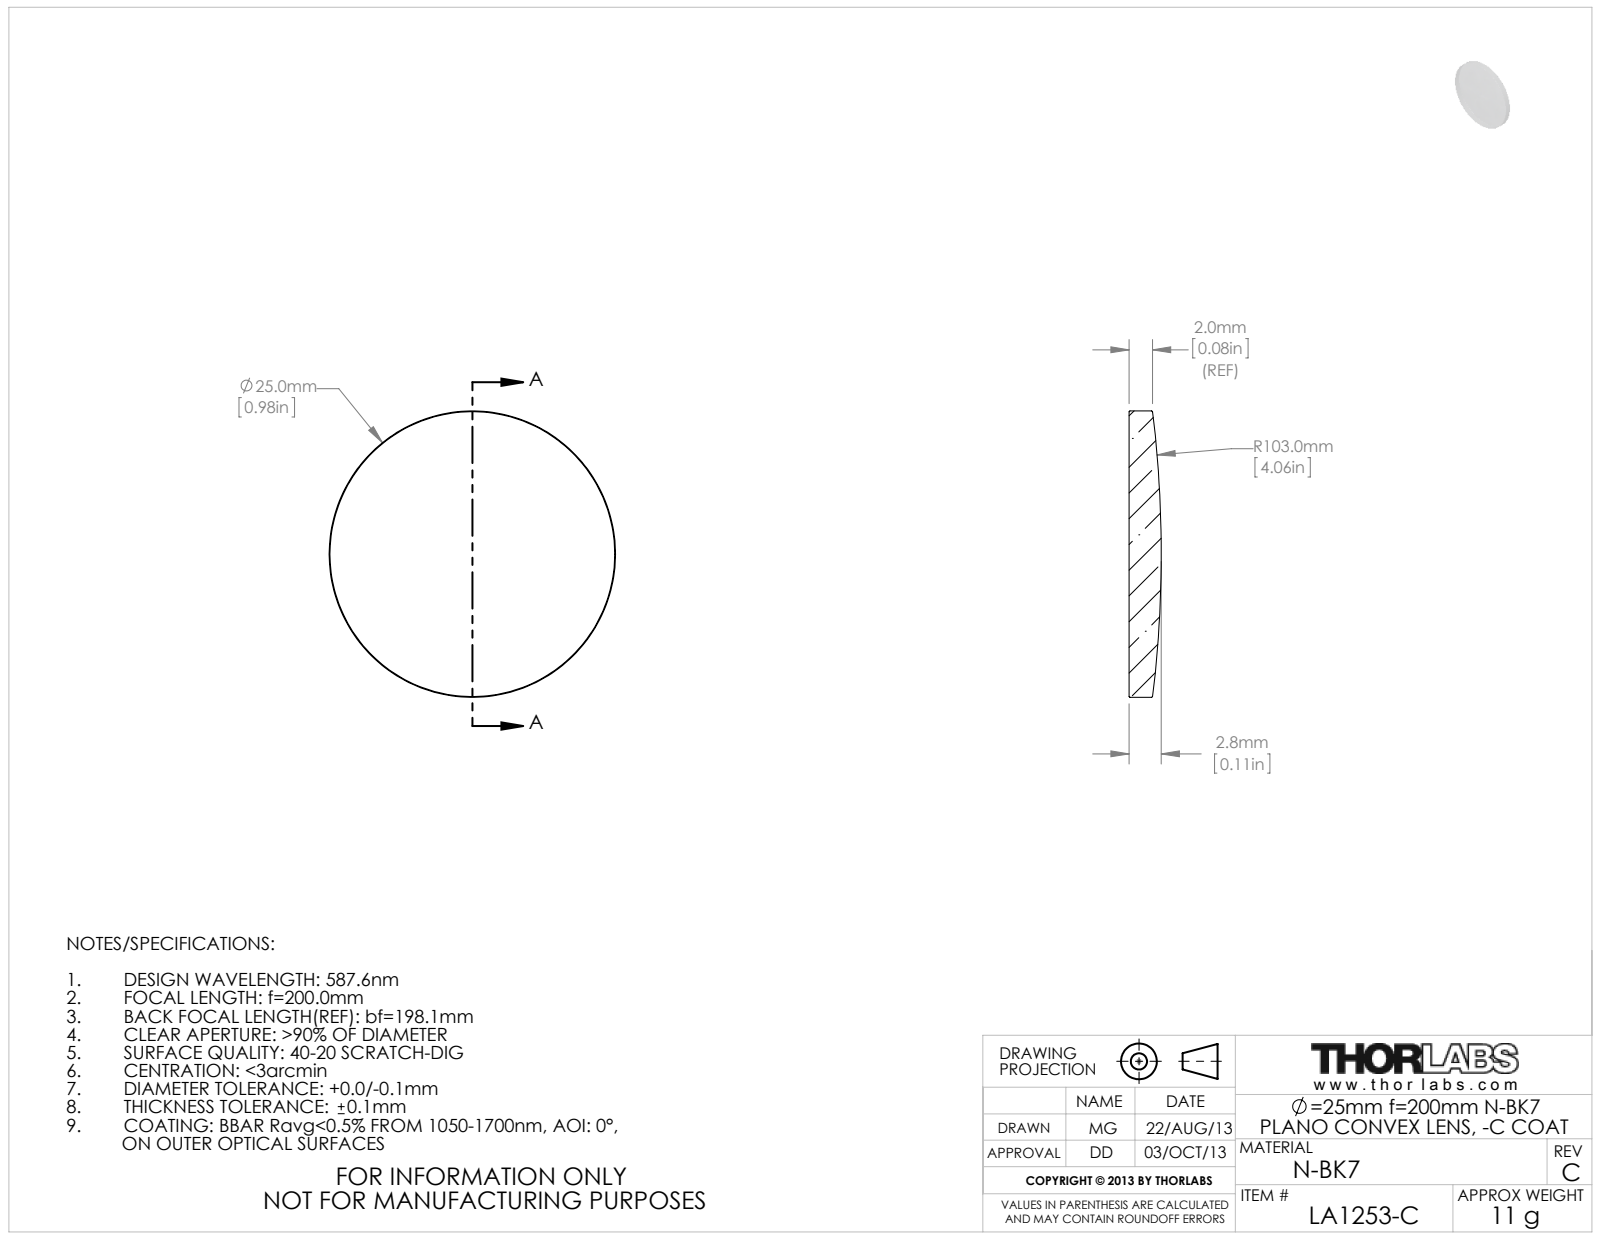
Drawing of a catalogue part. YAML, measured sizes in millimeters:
part_name: "19066-E0W"
step_written_by: "SolidWorks 2009 (AUTOMOTIVE_DESIGN)"
units: millimeters
bodies: {solids: 1, faces: 5, planar: 1, cylindrical: 2, other: 2}
overall_size: [25, 25, 2.8]
volume: 1188
surface_area: 1144
round_bosses_or_shafts:
  - {diameter: 25, count: 1}
